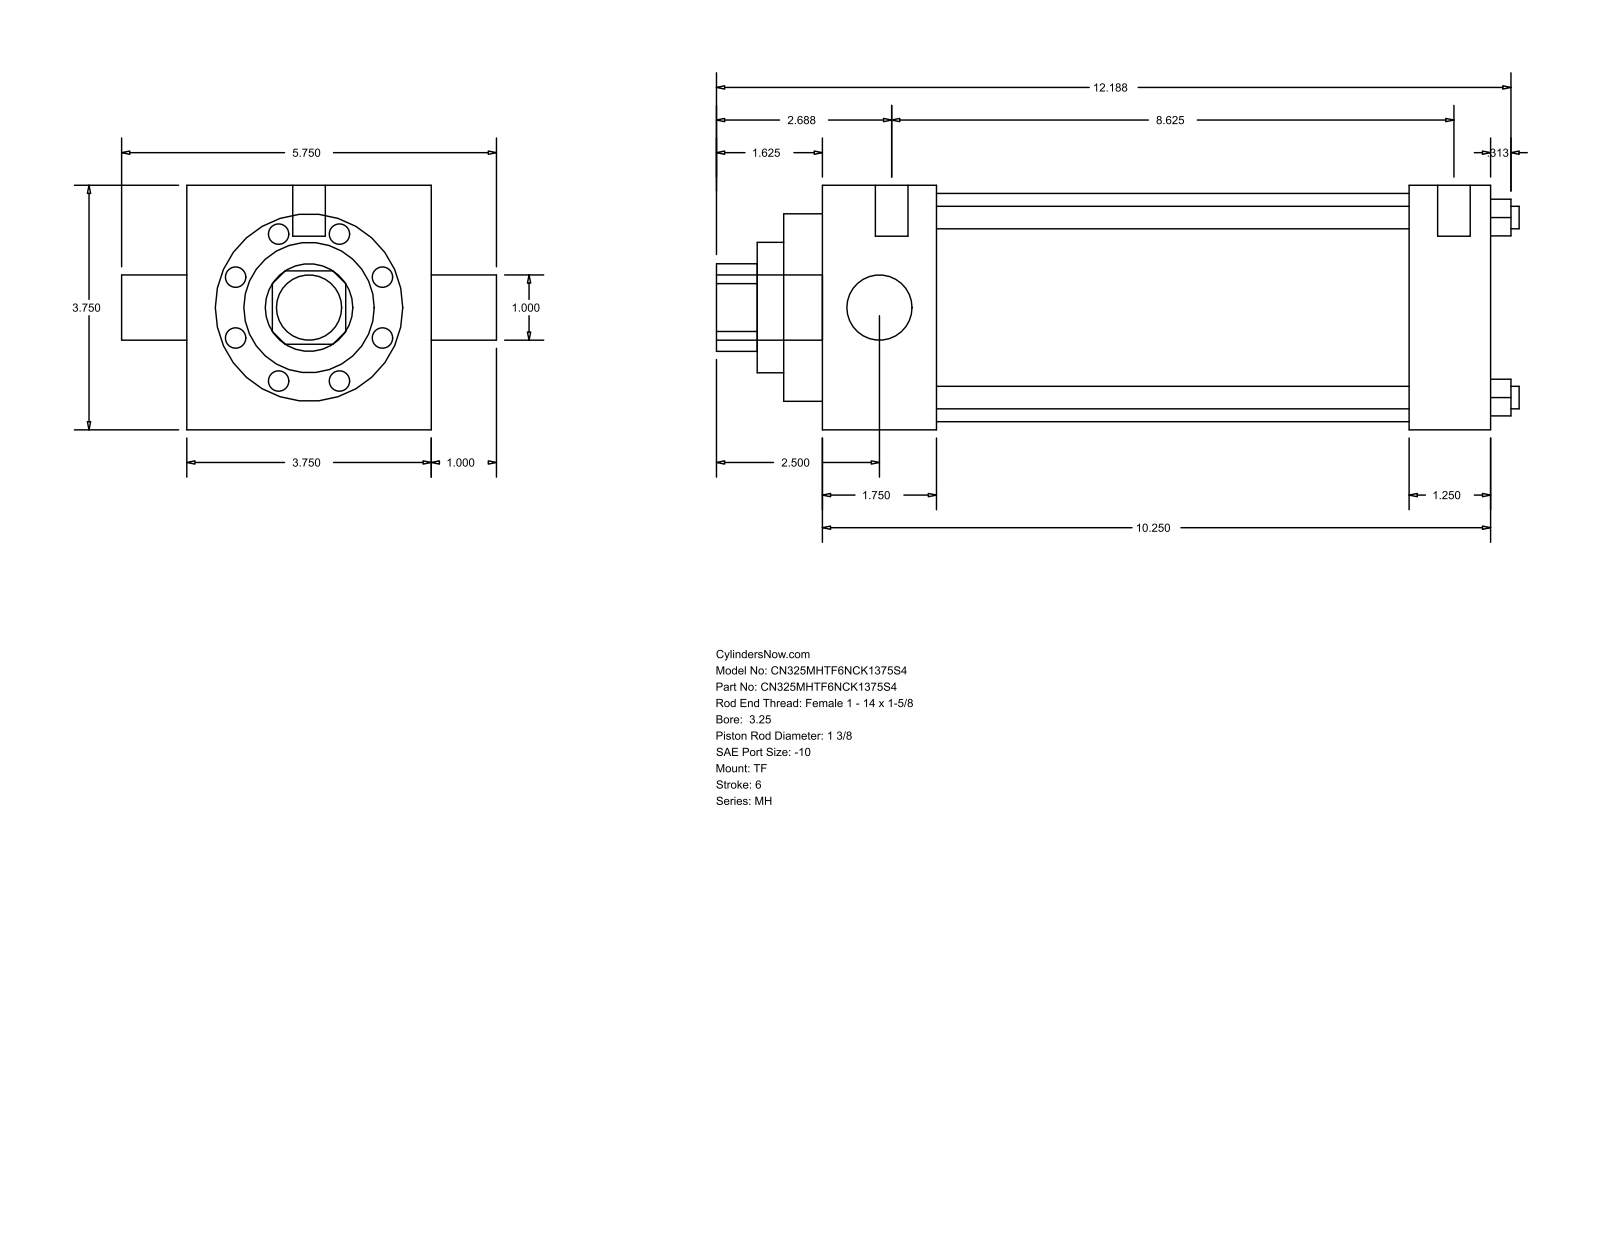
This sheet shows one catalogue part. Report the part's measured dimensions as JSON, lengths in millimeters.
{"part_name": "MH_TF__0325_1.375", "step_written_by": "GSSL Pune (CONFIG_CONTROL_DESIGN)", "units": "millimeters", "bodies": {"solids": 0, "faces": 86, "planar": 61, "cylindrical": 25, "other": 0}, "overall_size": [312.74, 146.05, 95.25], "round_holes": [[8.76, 4], [25.4, 1], [34.92, 1], [50.8, 1], [73.03, 1], [88.9, 1]], "round_bosses_or_shafts": [[5.56, 3], [12.7, 2], [25.4, 1]], "partial_cylinders_radius": [[17.06, 1]], "face_to_face_distances": [95.24, 260.35, 44.45, 228.61, 184.16, 215.9, 31.74, 15.08, 59.53, 243.69], "hole_center_spacings": [49.57, 70.1, 99.14]}
